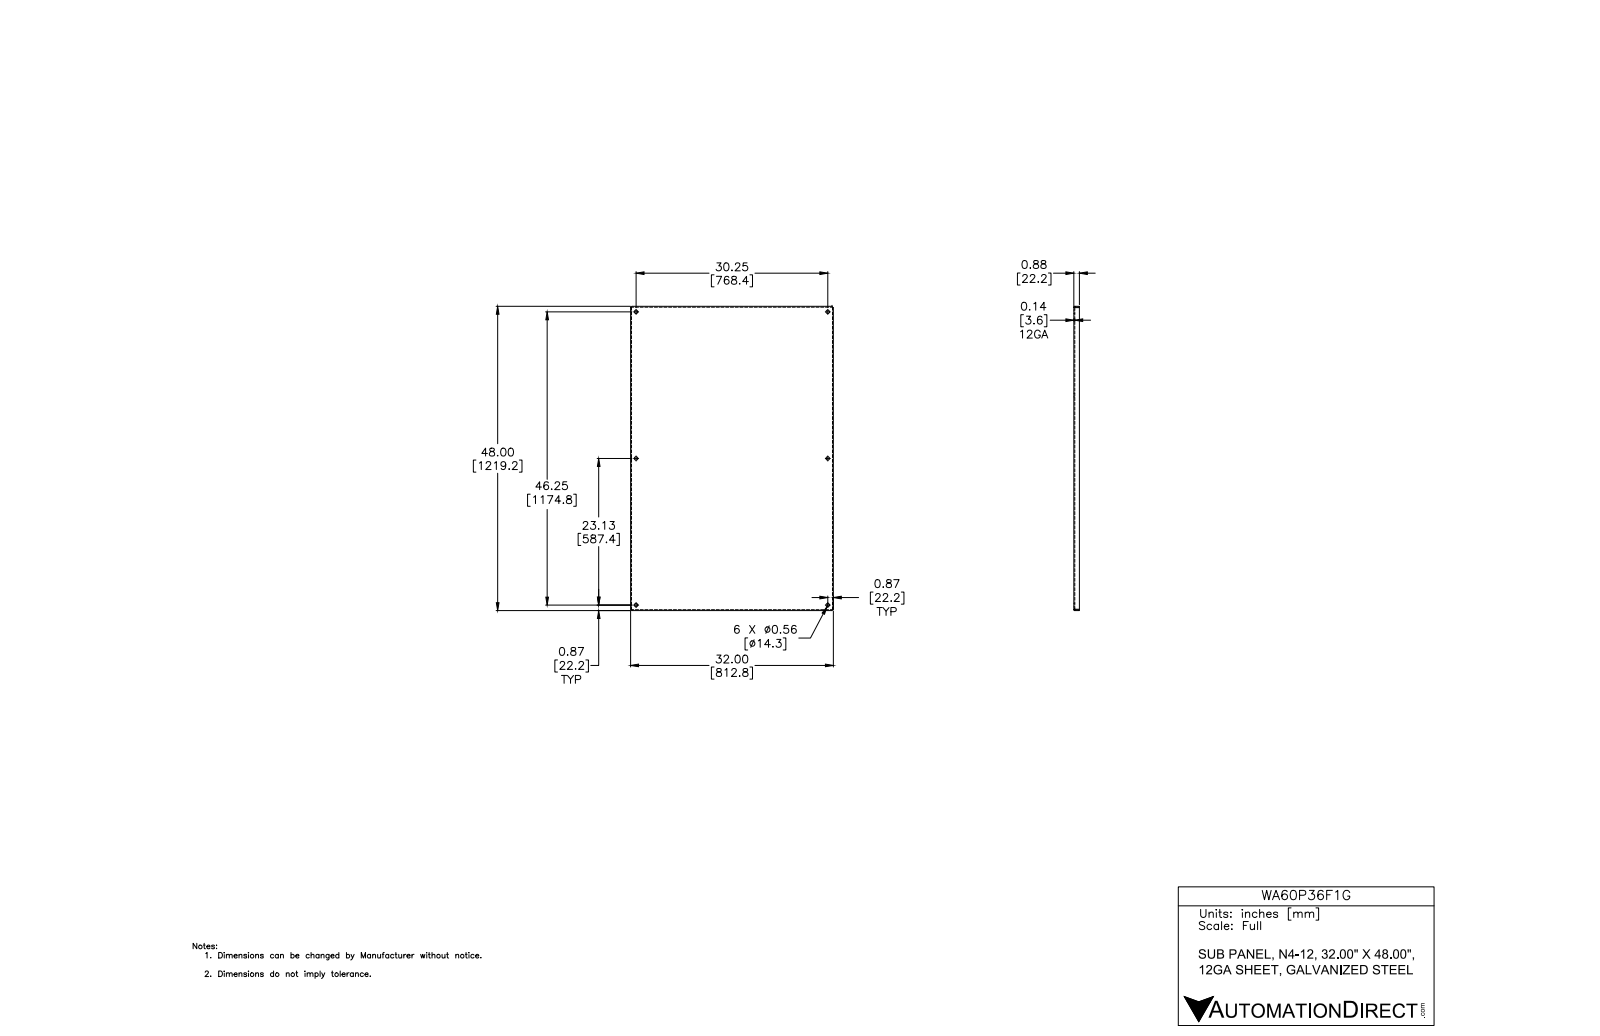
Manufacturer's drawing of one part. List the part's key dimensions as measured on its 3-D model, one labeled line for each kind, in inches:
Part name (STEP PRODUCT): WA_P_F_G
STEP written by: Autodesk Inventor 2012 (AUTOMOTIVE_DESIGN)
Units: inches
Bodies: 1 solid, 44 faces (22 planar, 14 cylindrical, 8 other)
Overall size (bounding box): 48 × 32 × 0.875
Volume: 155.1 in³ · Surface area: 3 325 in²
Round holes (diameter × count): ⌀0.563 ×6
Partial cylindrical surfaces — rounded edges, fillets, slot ends (radius × count): R0.016 ×4, R0.109 ×4
Main face-to-face distances: 0.094, 31.906, 47.906, 32, 31.813, 48, 47.813, 0.781, 0.875, 0.16
Hole centre spacings: 23.125, 23.125, 30.25, 38.077, 46.25, 55.264, 30.25, 38.076
